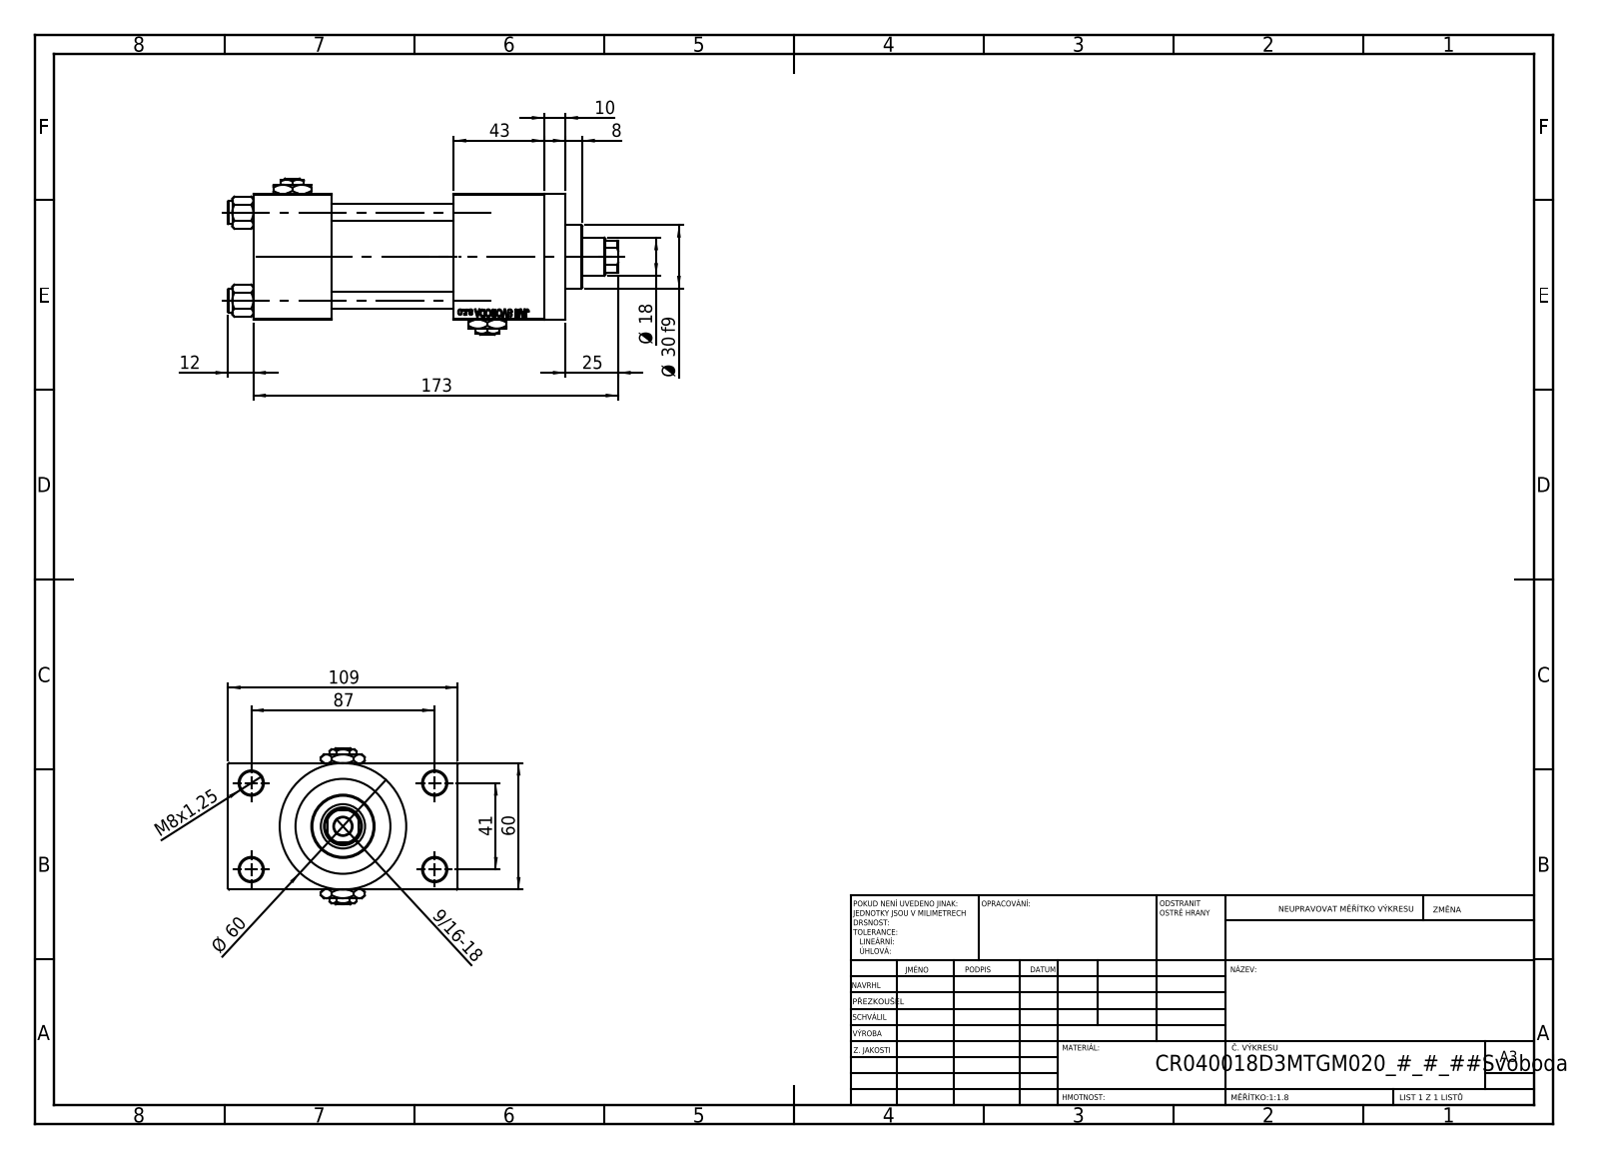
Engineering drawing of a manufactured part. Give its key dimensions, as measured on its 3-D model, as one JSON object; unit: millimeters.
{"part_name": "V215CR_VCP_D; V215_VC_A; NUT_M5_D; V215CR_D_TYCINKA (+2 more)", "step_written_by": "SolidWorks 2019 (CONFIG_CONTROL_DESIGN)", "units": "millimeters", "bodies": {"solids": 13, "faces": 1189, "planar": 542, "cylindrical": 89, "other": 558}, "overall_size": [185, 109, 74], "volume_mm3": 520654, "surface_area_mm2": 123078, "round_holes": [[8, 4], [11, 4], [7, 2], [16.66, 2], [24, 2], [8.5, 1], [18, 1], [21, 1], [31, 1], [40, 1], [45, 1]], "round_bosses_or_shafts": [[11, 4], [60, 1], [46, 1], [30, 1]], "partial_cylinders_radius": [[8.5, 1]], "face_to_face_distances": [60, 24.5, 84.5, 58, 37, 95, 43, 138, 101, 109], "hole_center_spacings": [22.65, 29.49, 41.7, 47.15, 48.09, 64.35, 76.49, 41]}
